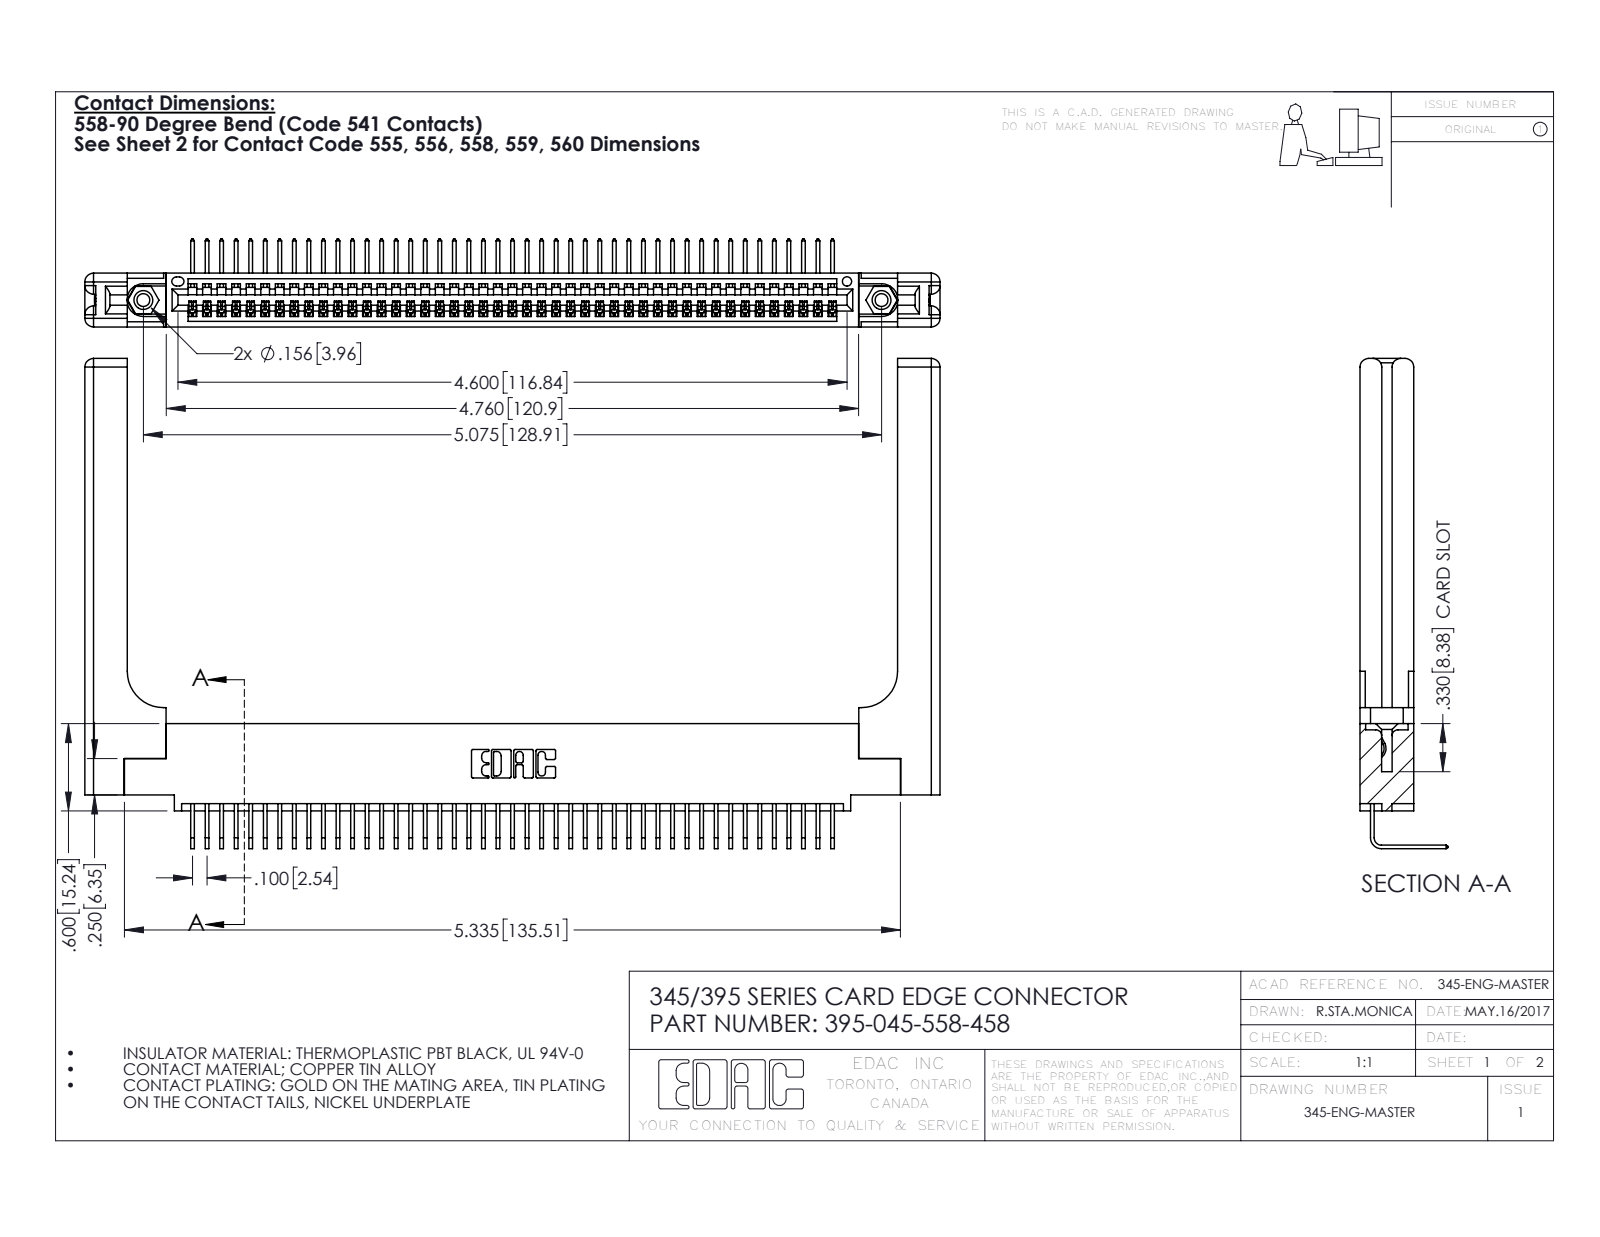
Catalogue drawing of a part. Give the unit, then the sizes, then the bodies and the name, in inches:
Units: inches
Overall size (bounding box): 5.879 × 3.369 × 0.605
Round holes (diameter × count): ⌀0.089 ×2, ⌀0.125 ×2, ⌀0.156 ×2, ⌀0.064 ×1
Round bosses / shafts (diameter × count): ⌀0.155 ×2
Partial cylindrical surfaces — rounded edges, fillets, slot ends (radius × count): R0.006 ×90, R0.01 ×22, R0.06 ×16, R0.007 ×6, R0.031 ×6, R0.026 ×3, R0.03 ×2, R0.031 ×2
Main face-to-face distances: 0.072, 0.37, 0.298, 0.098, 0.272, 0.025, 0.2, 0.225, 0.148, 0.15
Hole centre spacings: 0.27, 4.839, 5.075
Volume: 1.391 in³ · Surface area: 39.2 in²
Bodies: 50 solids, 3086 faces (2122 planar, 904 cylindrical, 60 other)
Part name (STEP PRODUCT): 395-045-558-458; 345-250-001_345-250-001-102; 345-220-058_345-220-058; 345-292-001_558 Tail - 2 (+1 more)
STEP written by: SolidWorks 2016 (CONFIG_CONTROL_DESIGN)
